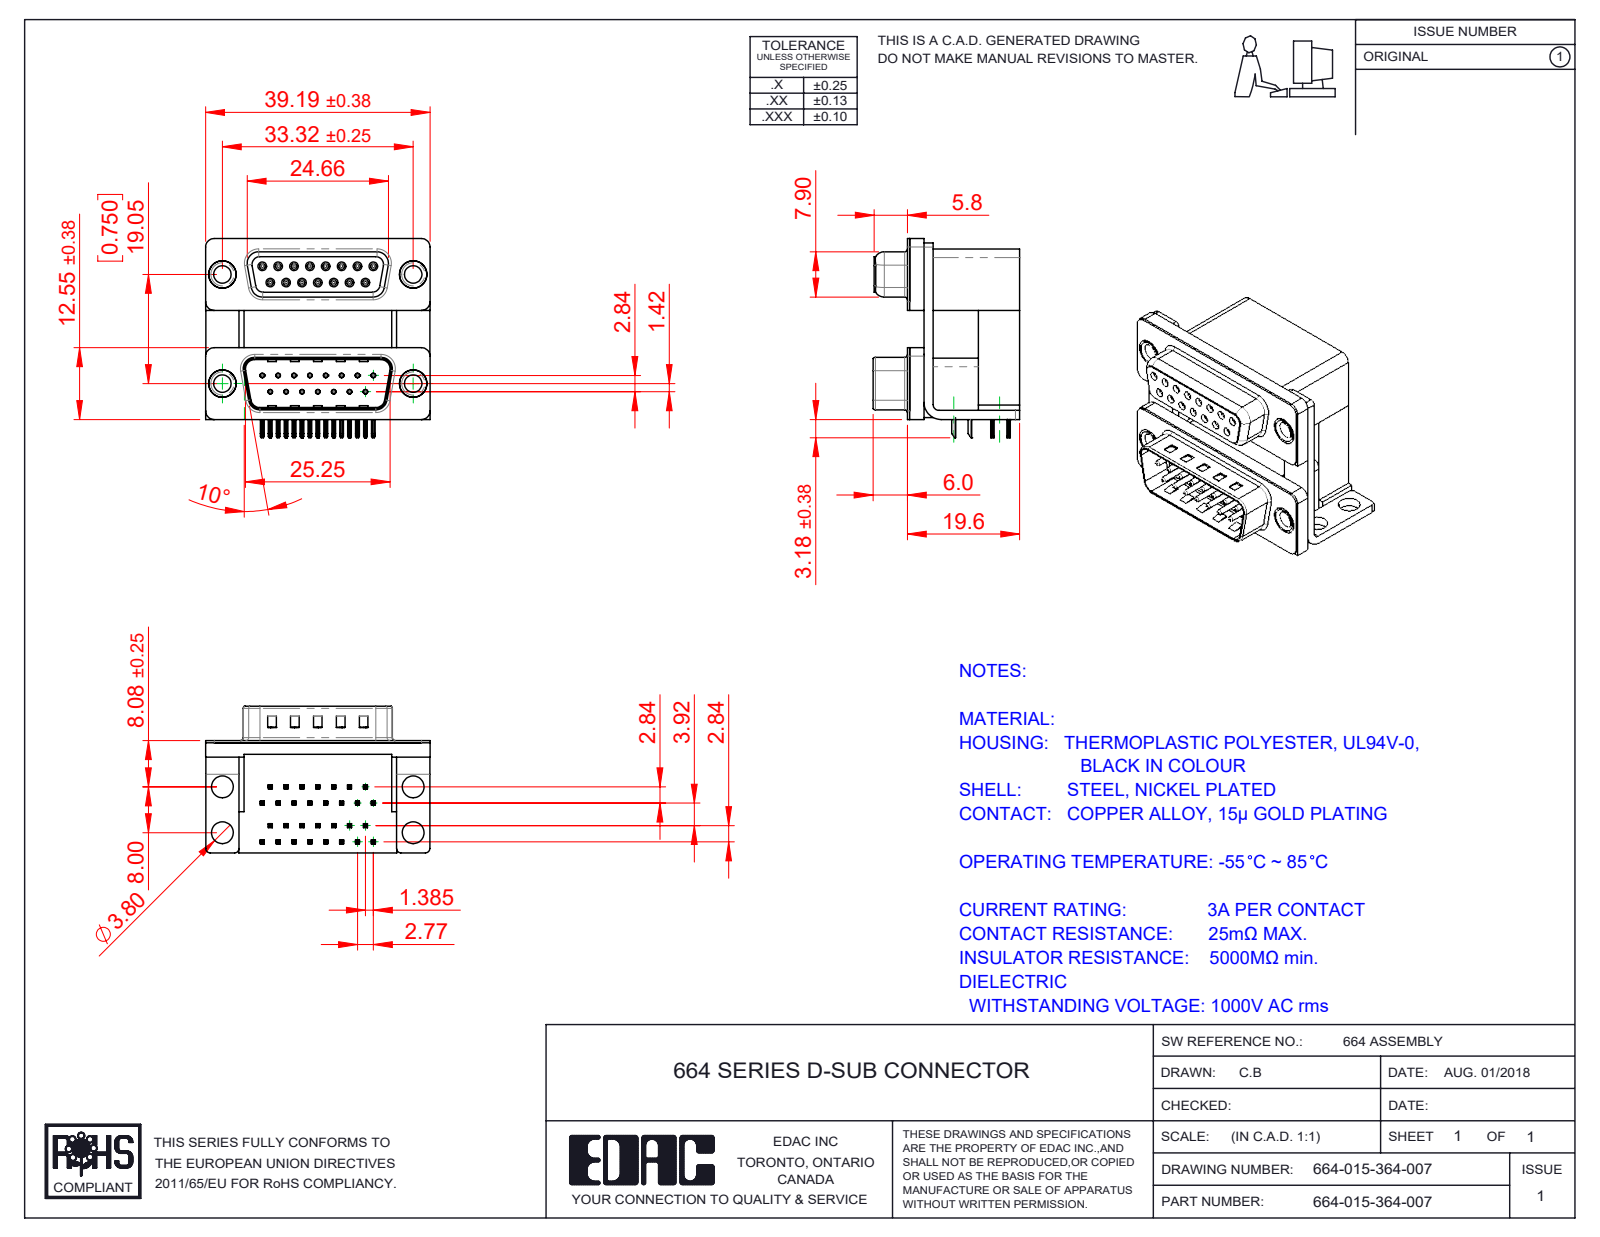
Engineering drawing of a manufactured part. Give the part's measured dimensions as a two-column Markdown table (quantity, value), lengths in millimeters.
| quantity | value |
| --- | --- |
| part name | 664 Mounting Bracket_NoneM; 664 Contact Top Upper_M; 664 Contact Top Lower; 664 Shell Plug_15 Contacts (+8 more) |
| STEP written by | SolidWorks 2020 (CONFIG_CONTROL_DESIGN) |
| units | millimeters |
| bodies | 41 solids, 3828 faces (2015 planar, 978 cylindrical, 835 other) |
| overall size | 39.19 × 34.78 × 25.6 |
| volume | 15 127 mm³ |
| surface area | 16 753 mm² |
| round holes (diameter × count) | 0.8 × 30, 0.35 × 15, 0.9 × 15, 3.05 × 4, 3.5 × 4, 3.8 × 4, 4 × 4, 4.8 × 4, 5 × 4 |
| round bosses / shafts (diameter × count) | 1.2 × 15, 0.75 × 15, 4.9 × 4, 4.75 × 4, 3.85 × 4 |
| partial cylindrical surfaces (radius × count) | 0.1 × 120, 0.15 × 60, 0.25 × 60, 0.12 × 30, 0.35 × 30, 1.5 × 16, 0.34 × 15, 0.5 × 12 |
| main face-to-face distances | 0.4, 19.2, 16.7, 2.5, 7.2, 12, 9.5, 10.69, 2.19, 2.9 |
| hole center spacings | 3.16, 2.77, 19.25, 5.54, 19.84, 8.31, 19.05, 20.78 |
